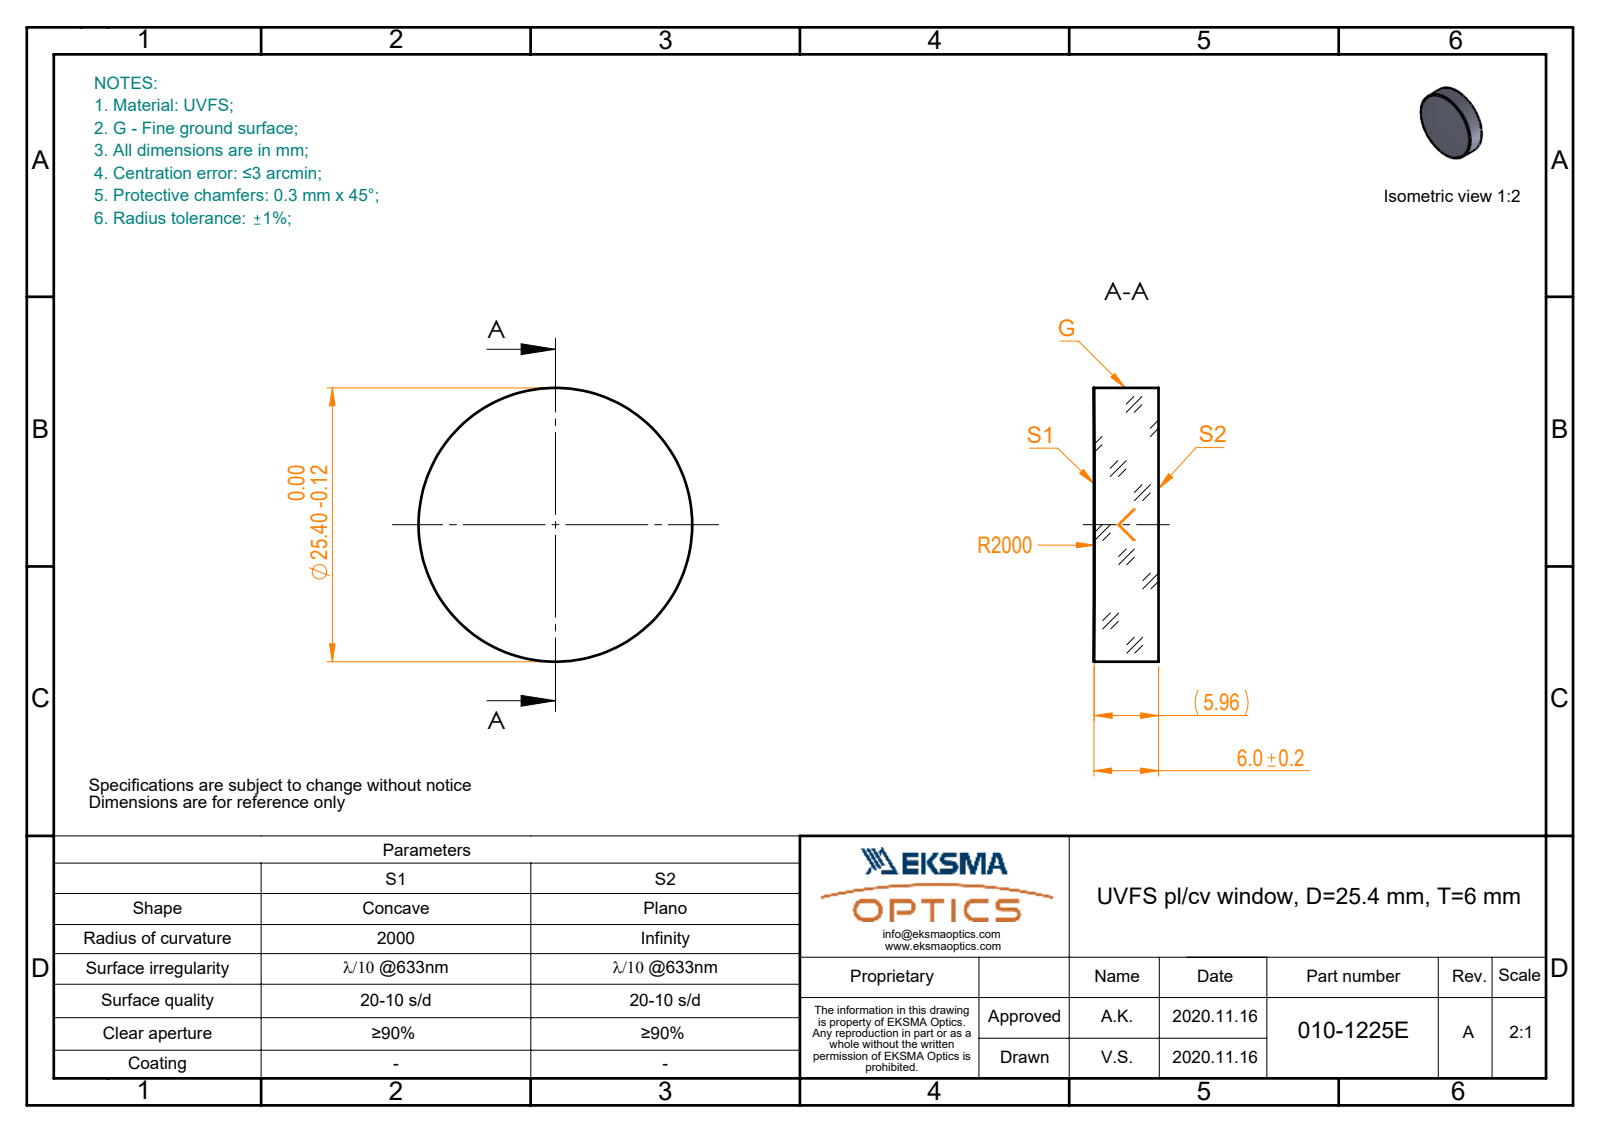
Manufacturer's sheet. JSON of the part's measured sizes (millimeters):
{"part_name": "010-1225E_UVFS_PCV_window", "step_written_by": "SolidWorks 2019 (CONFIG_CONTROL_DESIGN)", "units": "millimeters", "bodies": {"solids": 1, "faces": 5, "planar": 1, "cylindrical": 2, "other": 2}, "overall_size": [25.4, 25.4, 6], "volume_mm3": 3030, "surface_area_mm2": 1492, "round_bosses_or_shafts": [[25.4, 1]]}
